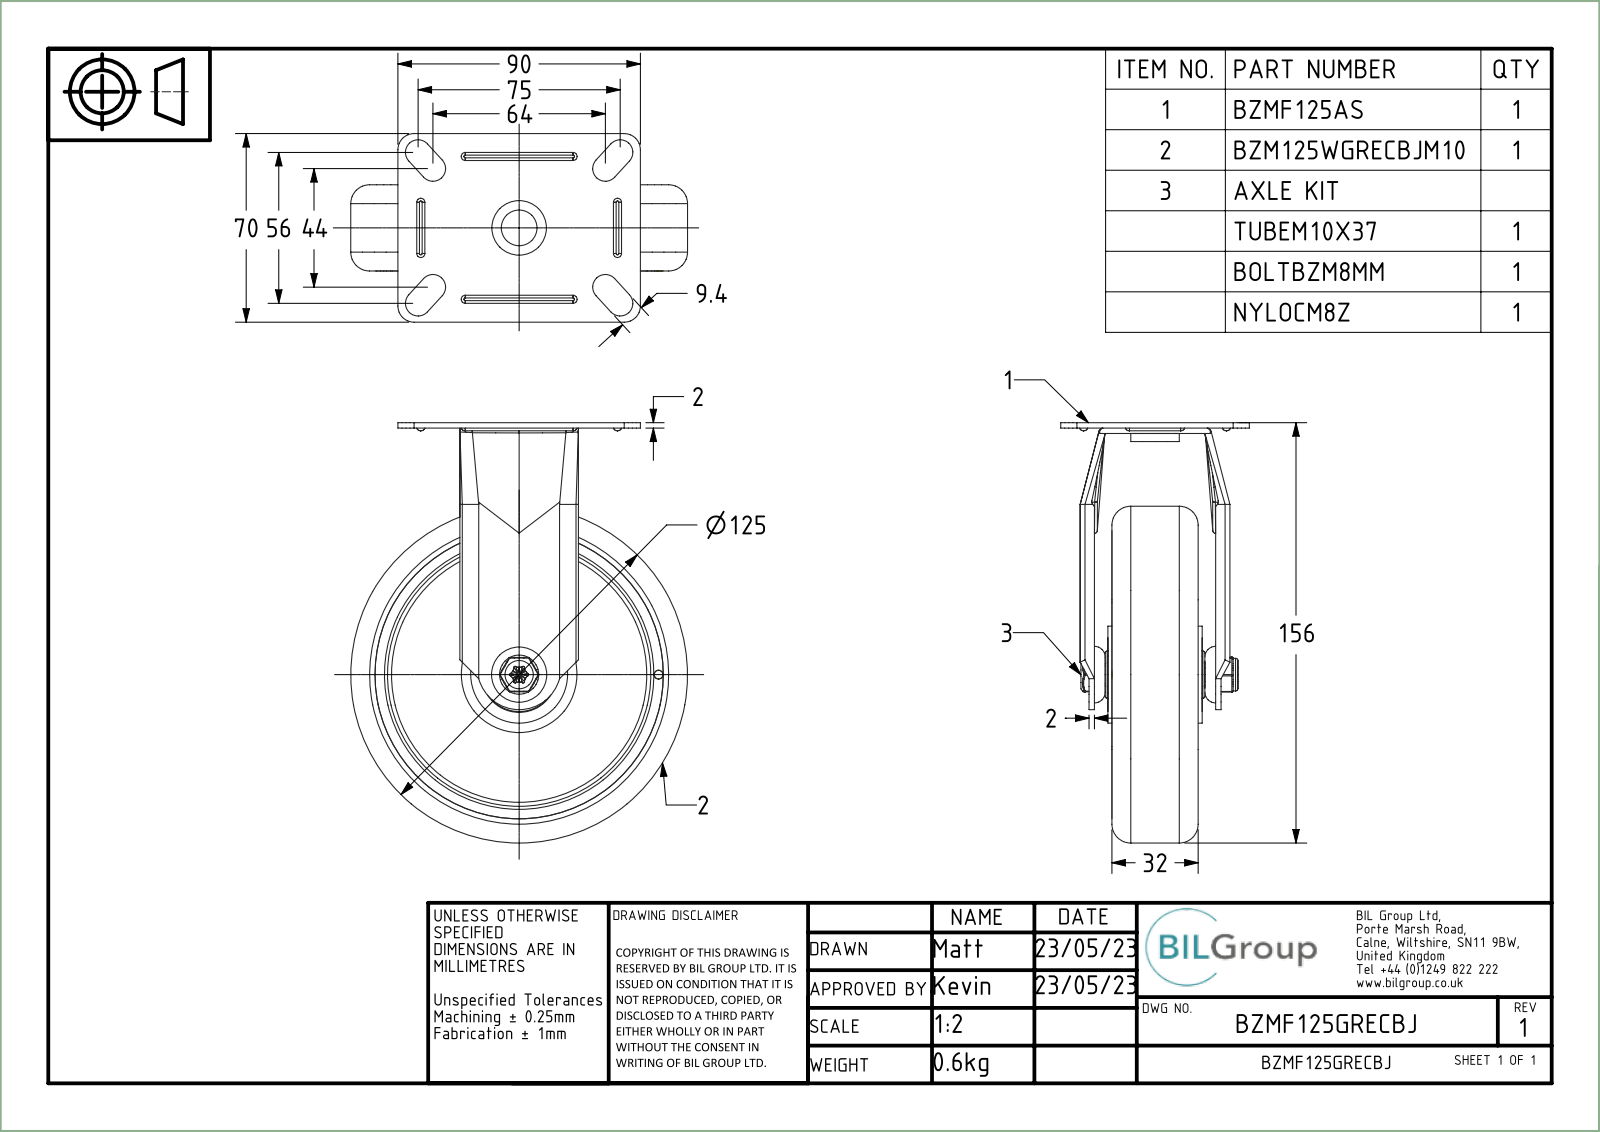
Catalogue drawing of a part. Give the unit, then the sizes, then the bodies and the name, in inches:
Units: inches
Overall size (bounding box): 6.142 × 4.921 × 2.756
Round holes (diameter × count): ⌀0.709 ×2, ⌀0.128 ×1, ⌀0.315 ×1, ⌀0.323 ×1, ⌀0.327 ×1, ⌀0.339 ×1, ⌀0.398 ×1, ⌀0.409 ×1, ⌀0.522 ×1, ⌀0.866 ×1, ⌀1.004 ×1, ⌀1.102 ×1
Round bosses / shafts (diameter × count): ⌀4.921 ×1, ⌀1.417 ×1, ⌀0.689 ×1, ⌀0.591 ×1, ⌀0.476 ×1, ⌀0.394 ×1, ⌀0.236 ×1
Partial cylindrical surfaces — rounded edges, fillets, slot ends (radius × count): R0.02 ×30, R0.079 ×12, R0.039 ×8, R0.059 ×8, R0.185 ×8, R0.236 ×4, R0.108 ×1, R0.611 ×1
Main face-to-face distances: 0.079, 0.197, 0.787, 0.531, 0.728, 0.256, 1.85, 0.866, 0.335, 1.063
Hole centre spacings: 2.037
Volume: 14.5 in³ · Surface area: 180.9 in²
Bodies: 27 solids, 590 faces (133 planar, 215 cylindrical, 242 other)
Part name (STEP PRODUCT): BZMF125AS; ZINC PLATED PRESSED STEEL TOP PLATE; ZINC PLATED PRESSED STEEL FORKS; BZMF125GRECBJ (+8 more)
STEP written by: Spatial InterOp 3D (CONFIG_CONTROL_DESIGN)
